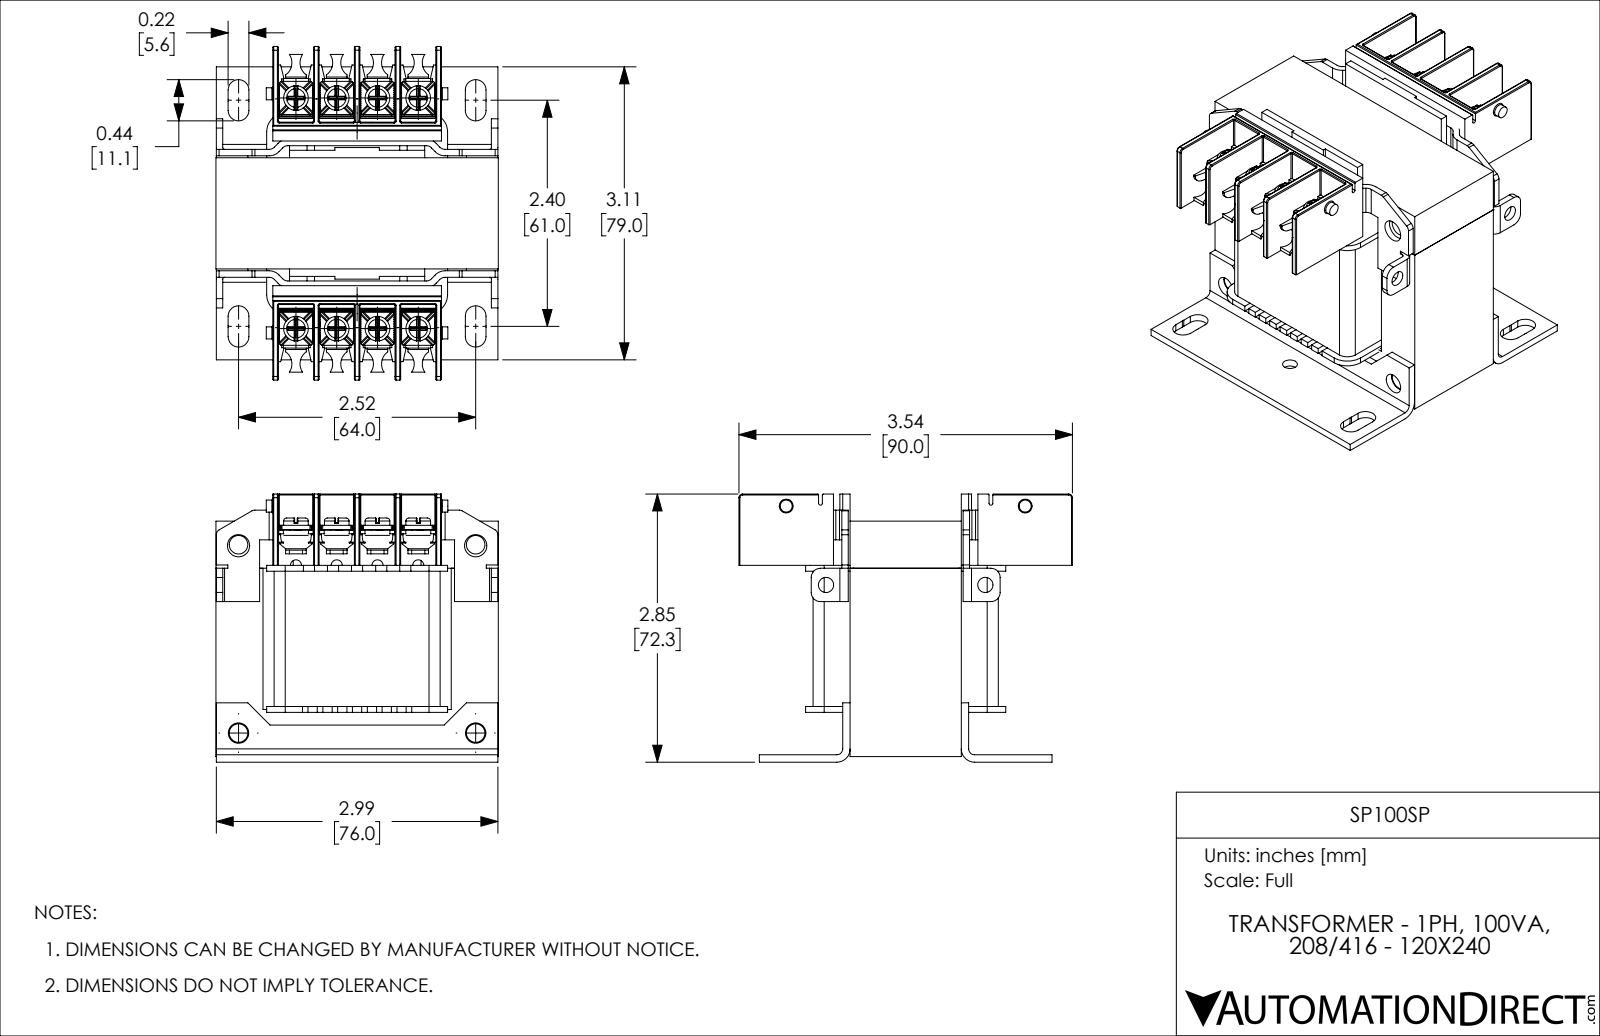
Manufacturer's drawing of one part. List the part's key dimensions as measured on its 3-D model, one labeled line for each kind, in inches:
Part name (STEP PRODUCT): SP100SP
STEP written by: SolidWorks 2018 (AUTOMOTIVE_DESIGN)
Units: inches
Bodies: 41 solids, 3166 faces (1936 planar, 935 cylindrical, 295 other)
Overall size (bounding box): 3.543 × 3 × 2.847
Volume: 12.71 in³ · Surface area: 134.6 in²
Round holes (diameter × count): ⌀0.157 ×10, ⌀0.105 ×8, ⌀0.138 ×8, ⌀0.197 ×4, ⌀0.161 ×2, ⌀0.217 ×2, ⌀0.236 ×2
Round bosses / shafts (diameter × count): ⌀0.262 ×8, ⌀0.24 ×8, ⌀0.168 ×8, ⌀0.11 ×8, ⌀0.128 ×3
Partial cylindrical surfaces — rounded edges, fillets, slot ends (radius × count): R0.005 ×52, R0.01 ×52, R0.012 ×48, R0.029 ×32, R0.059 ×18, R0.157 ×16, R0.035 ×12, R0.079 ×10
Main face-to-face distances: 0.5, 0.059, 2, 1.181, 0.433, 0.079, 2.5, 0.374, 0.866, 0.02
Hole centre spacings: 0.433, 0.866, 2.477, 1.299, 2.439, 2.588, 2.467, 2.487
